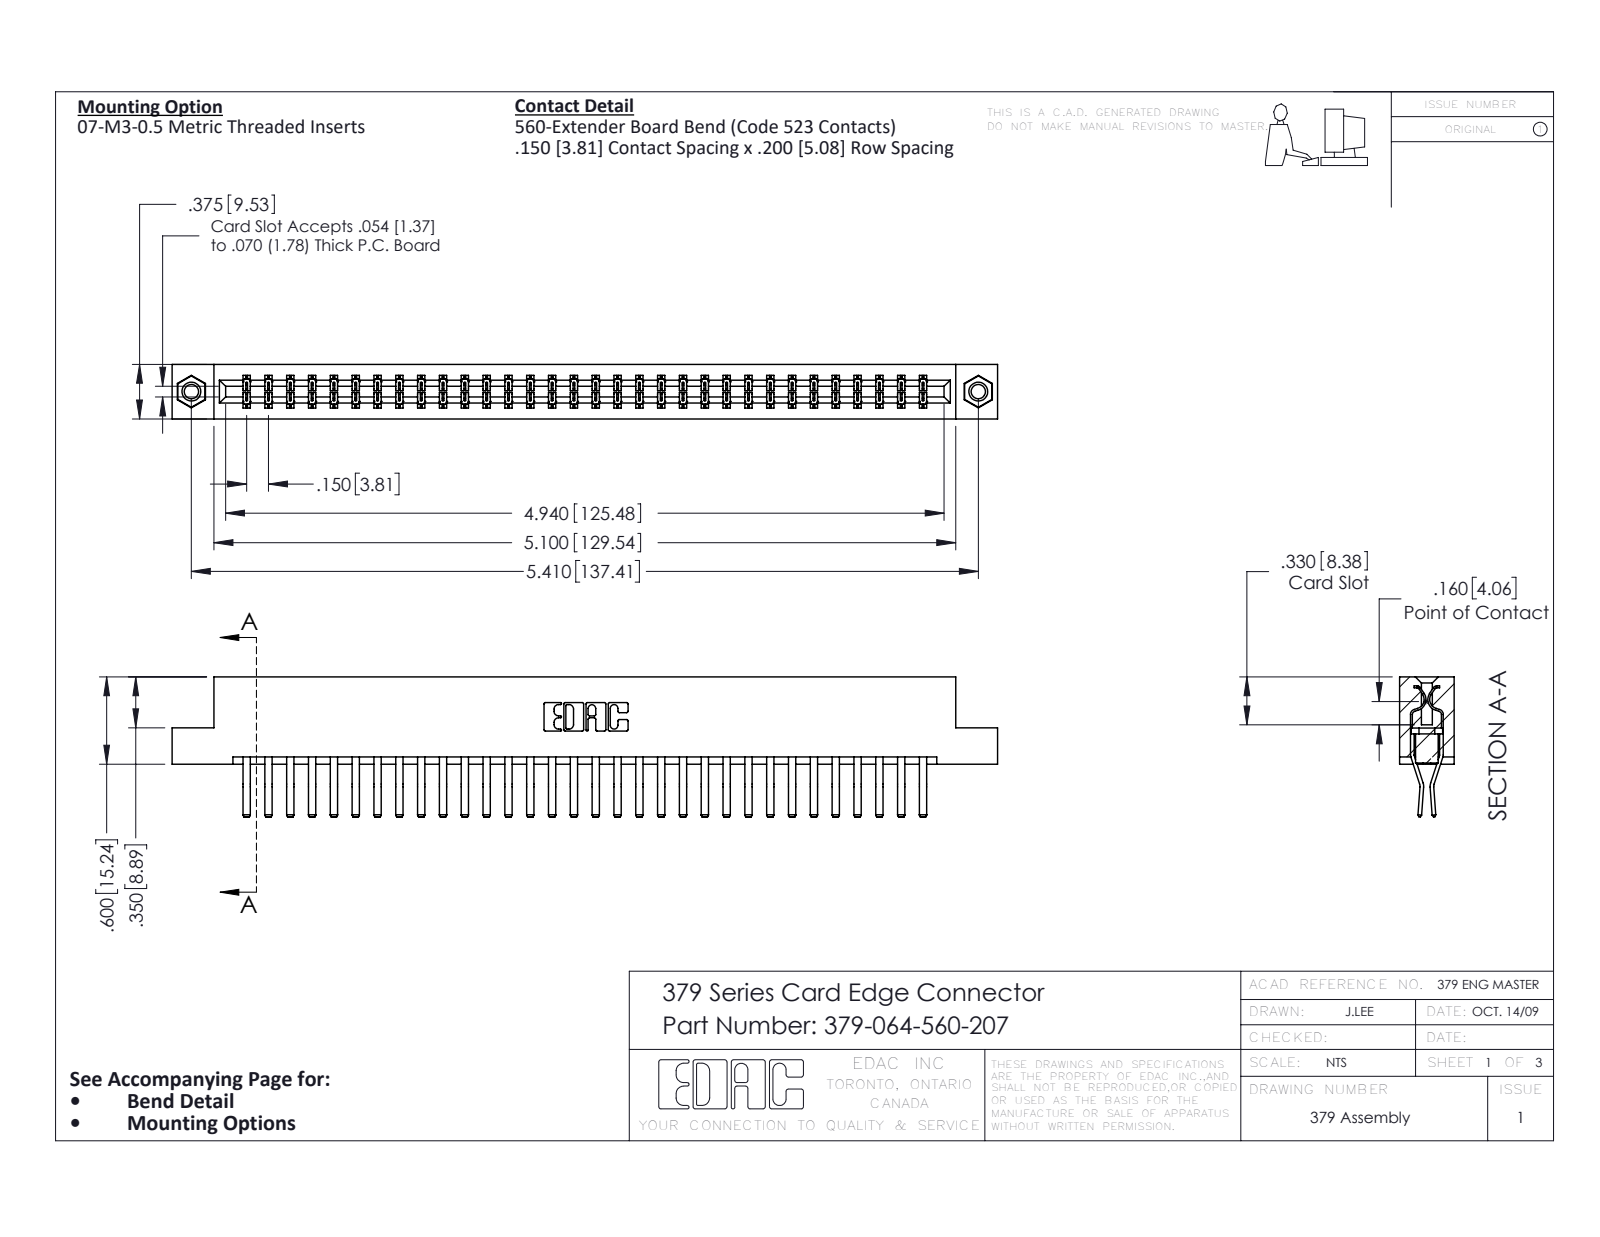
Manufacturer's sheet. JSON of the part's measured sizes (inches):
{"part_name": "345-250-001_345-250-005-103; 345-292-001_560 Tail; 379-064-560-207; 379 Part_Flush - .156 Dia - TI", "step_written_by": "SolidWorks 2016 (CONFIG_CONTROL_DESIGN)", "units": "inches", "bodies": {"solids": 67, "faces": 3630, "planar": 2406, "cylindrical": 1208, "other": 16}, "overall_size": [5.675, 0.962, 0.375], "volume_in3": 0.954, "surface_area_in2": 29.03, "round_holes": [[0.098, 2], [0.125, 2], [0.156, 2]], "round_bosses_or_shafts": [[0.155, 2]], "partial_cylinders_radius": [[0.006, 96], [0.01, 22], [0.007, 6], [0.031, 6], [0.026, 3], [0.01, 2], [0.014, 2], [0.022, 2]], "face_to_face_distances": [0.3, 0.075, 0.375, 0.6, 0.225, 0.025, 0.15, 0.45, 0.2, 0.15], "hole_center_spacings": [5.41]}
